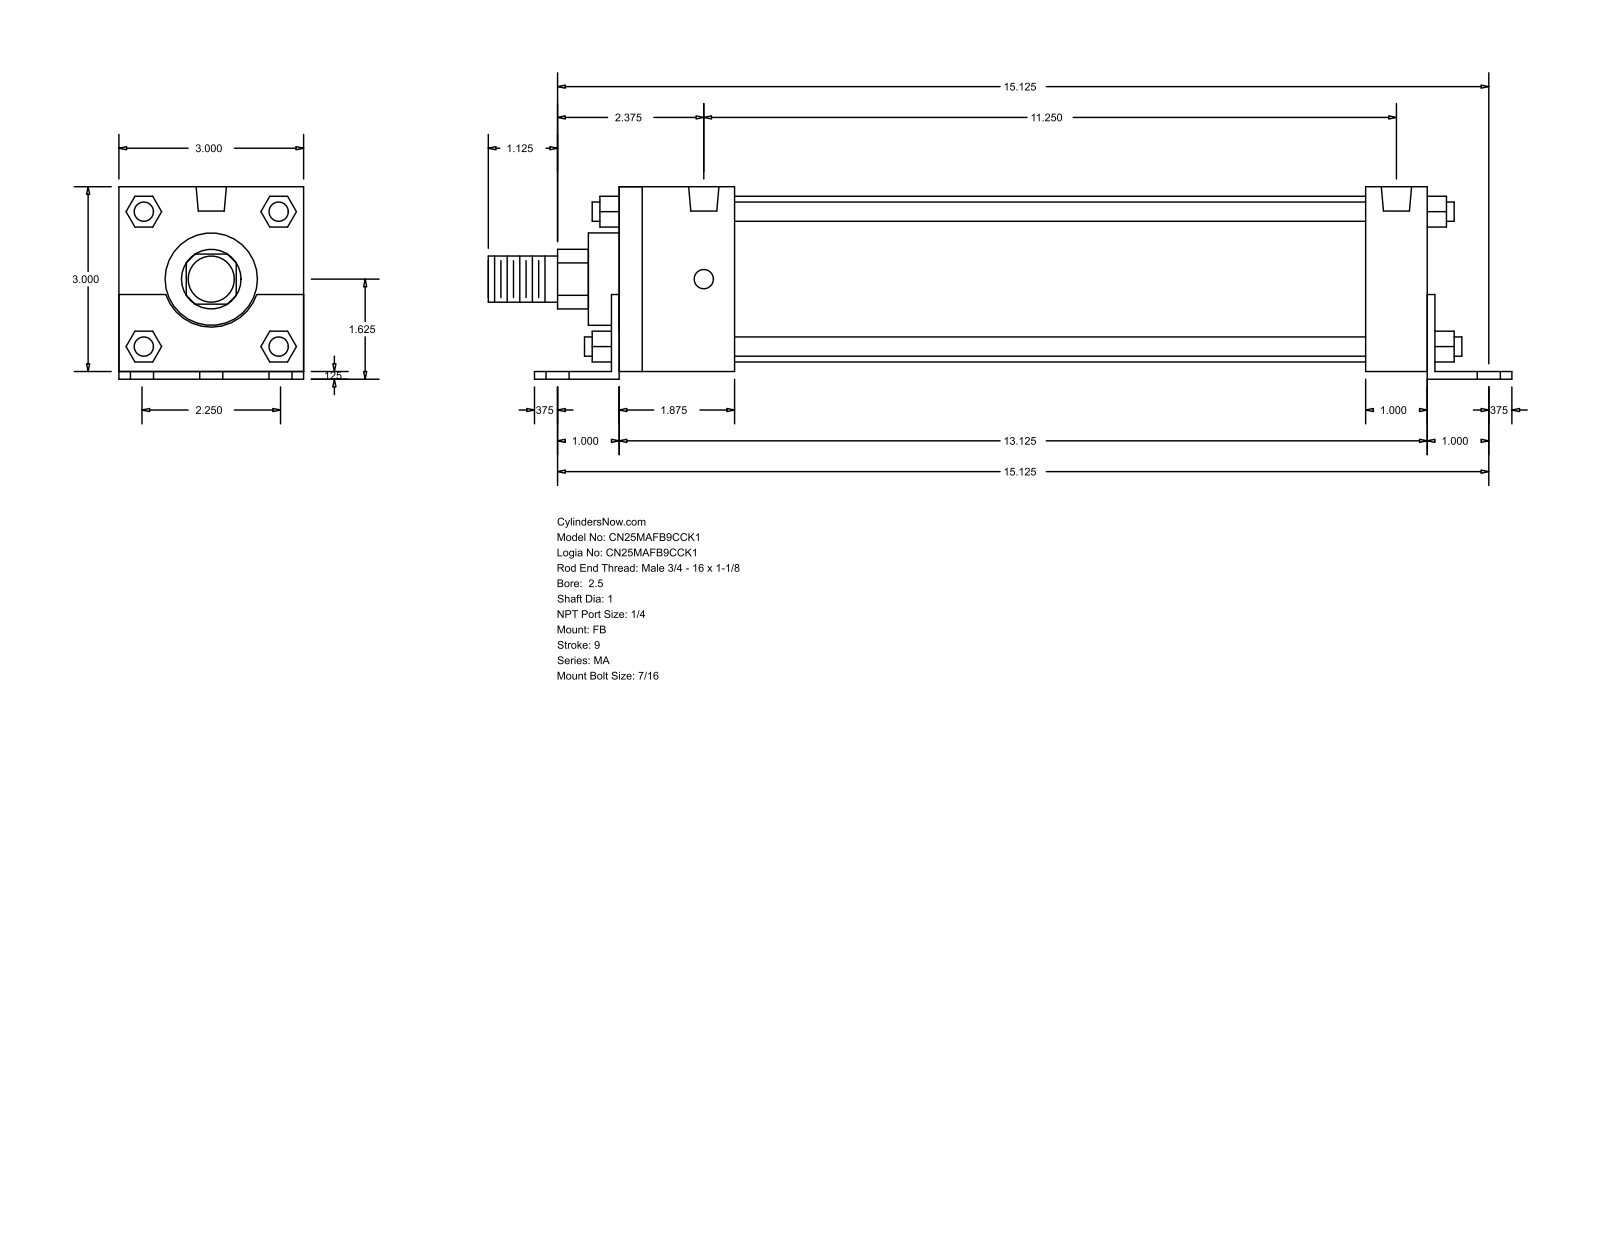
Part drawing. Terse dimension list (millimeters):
name: MA_FB__0250_1
written by: GSSL Pune (CONFIG_CONTROL_DESIGN)
unit: mm
bodies: 0 solids, 140 faces (105 planar, 35 cylindrical, 0 other)
size: 422.27 × 79.38 × 76.2
holes: 6× ⌀11.11, 4× ⌀7.94, 2× ⌀12.49
bosses: 4× ⌀7.94, 1× ⌀68.33, 1× ⌀38.1, 1× ⌀25.4, 1× ⌀19.05
rounds: 1× R12.29, 1× R19.81
face distances: 76.2, 3.17, 79.37, 333.37, 3.18, 12.7, 336.55, 28.57, 50.8, 47.63
hole spacings: 28.57, 385.24, 384.18, 47.63, 57.14, 66.75, 285.74, 325.11
